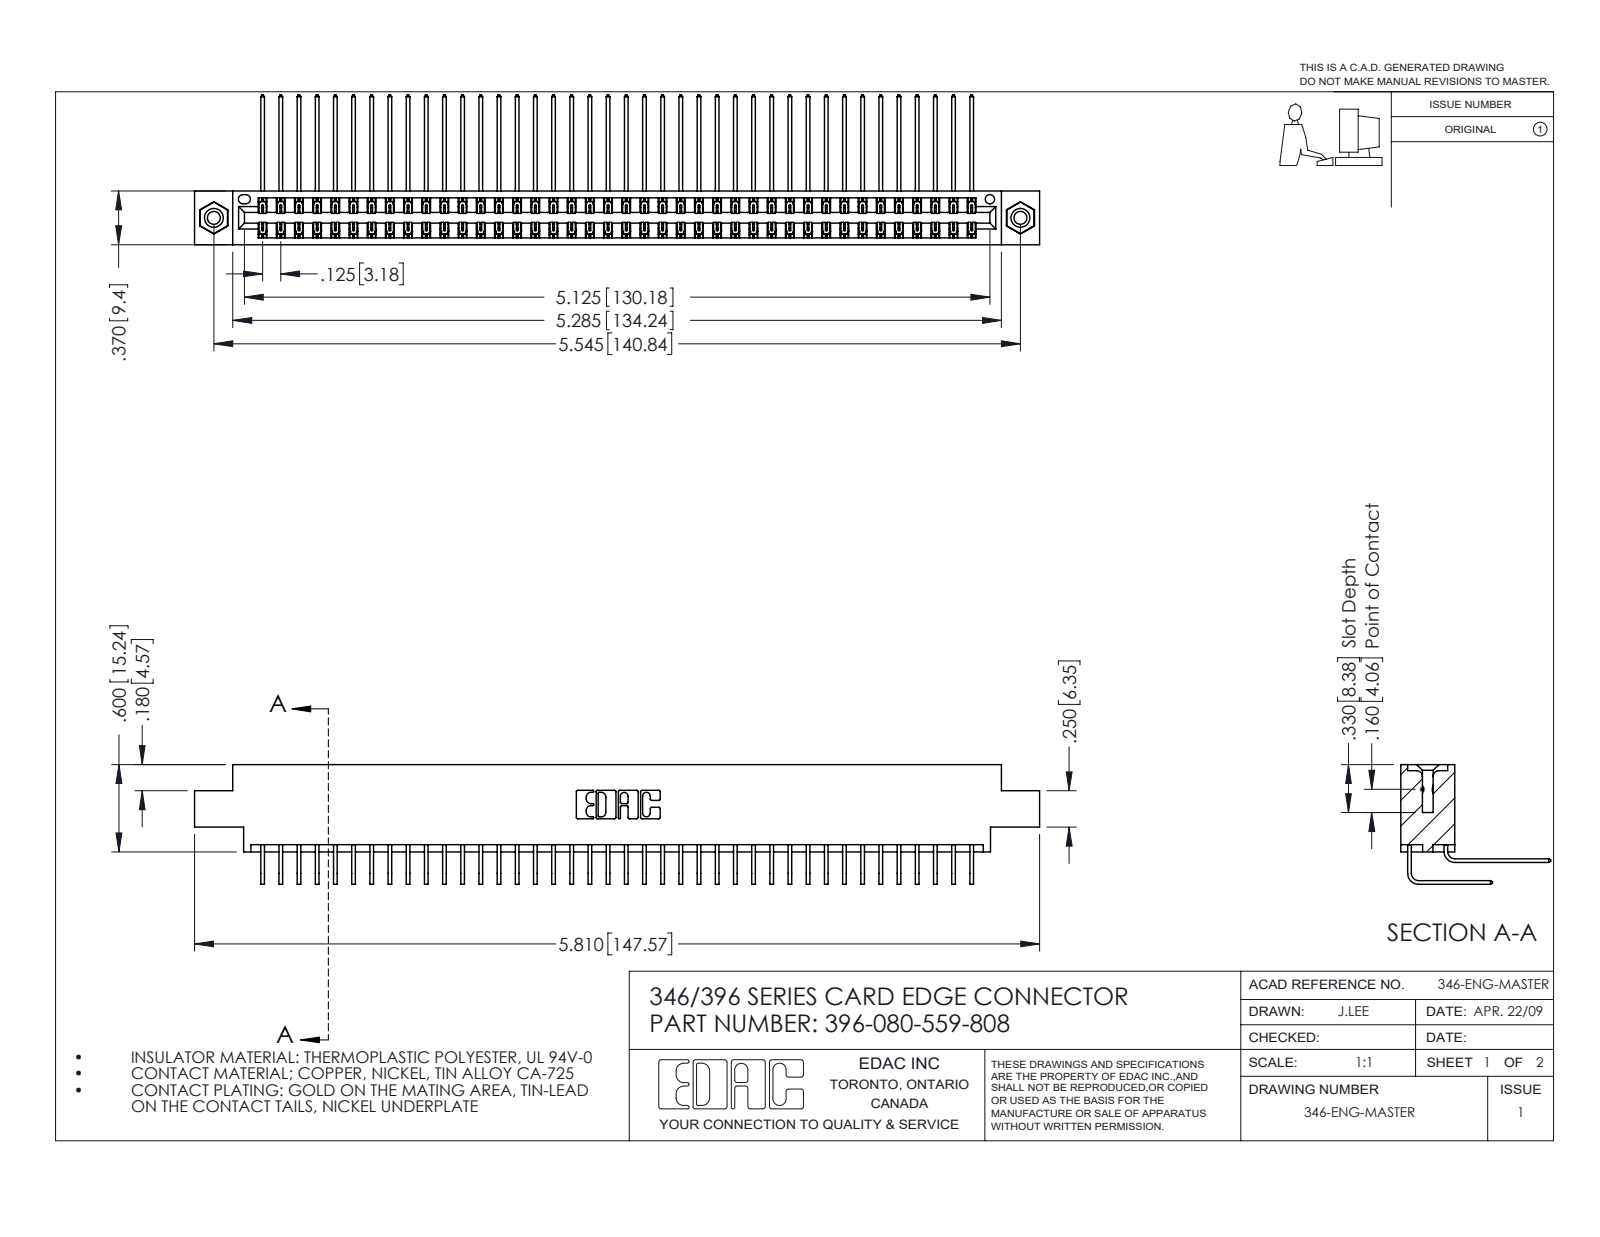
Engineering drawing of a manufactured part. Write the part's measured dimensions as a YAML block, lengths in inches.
part_name: "345-292-001_559 Tail - 2; 345-292-001_558 559 Tail - 1; 346 Part_0.170 Offset - 0.156 Dia-TI; 396-080-559-808 (+1 more)"
step_written_by: "SolidWorks 2016 (CONFIG_CONTROL_DESIGN)"
units: inches
bodies: {solids: 83, faces: 4506, planar: 3072, cylindrical: 1418, other: 16}
overall_size: [5.81, 1.03, 0.823]
volume: 0.896
surface_area: 34.96
round_holes:
  - {diameter: 0.089, count: 2}
  - {diameter: 0.125, count: 2}
  - {diameter: 0.156, count: 2}
  - {diameter: 0.064, count: 1}
round_bosses_or_shafts:
  - {diameter: 0.155, count: 2}
partial_cylinders:
  - {radius: 0.006, count: 120}
  - {radius: 0.01, count: 22}
  - {radius: 0.007, count: 6}
  - {radius: 0.031, count: 6}
  - {radius: 0.026, count: 3}
  - {radius: 0.014, count: 2}
  - {radius: 0.022, count: 2}
  - {radius: 0.024, count: 2}
face_to_face_distances: [0.048, 0.322, 0.025, 0.37, 0.25, 0.072, 0.298, 0.275, 0.222, 0.148]
hole_center_spacings: [0.246, 5.336, 5.545]
